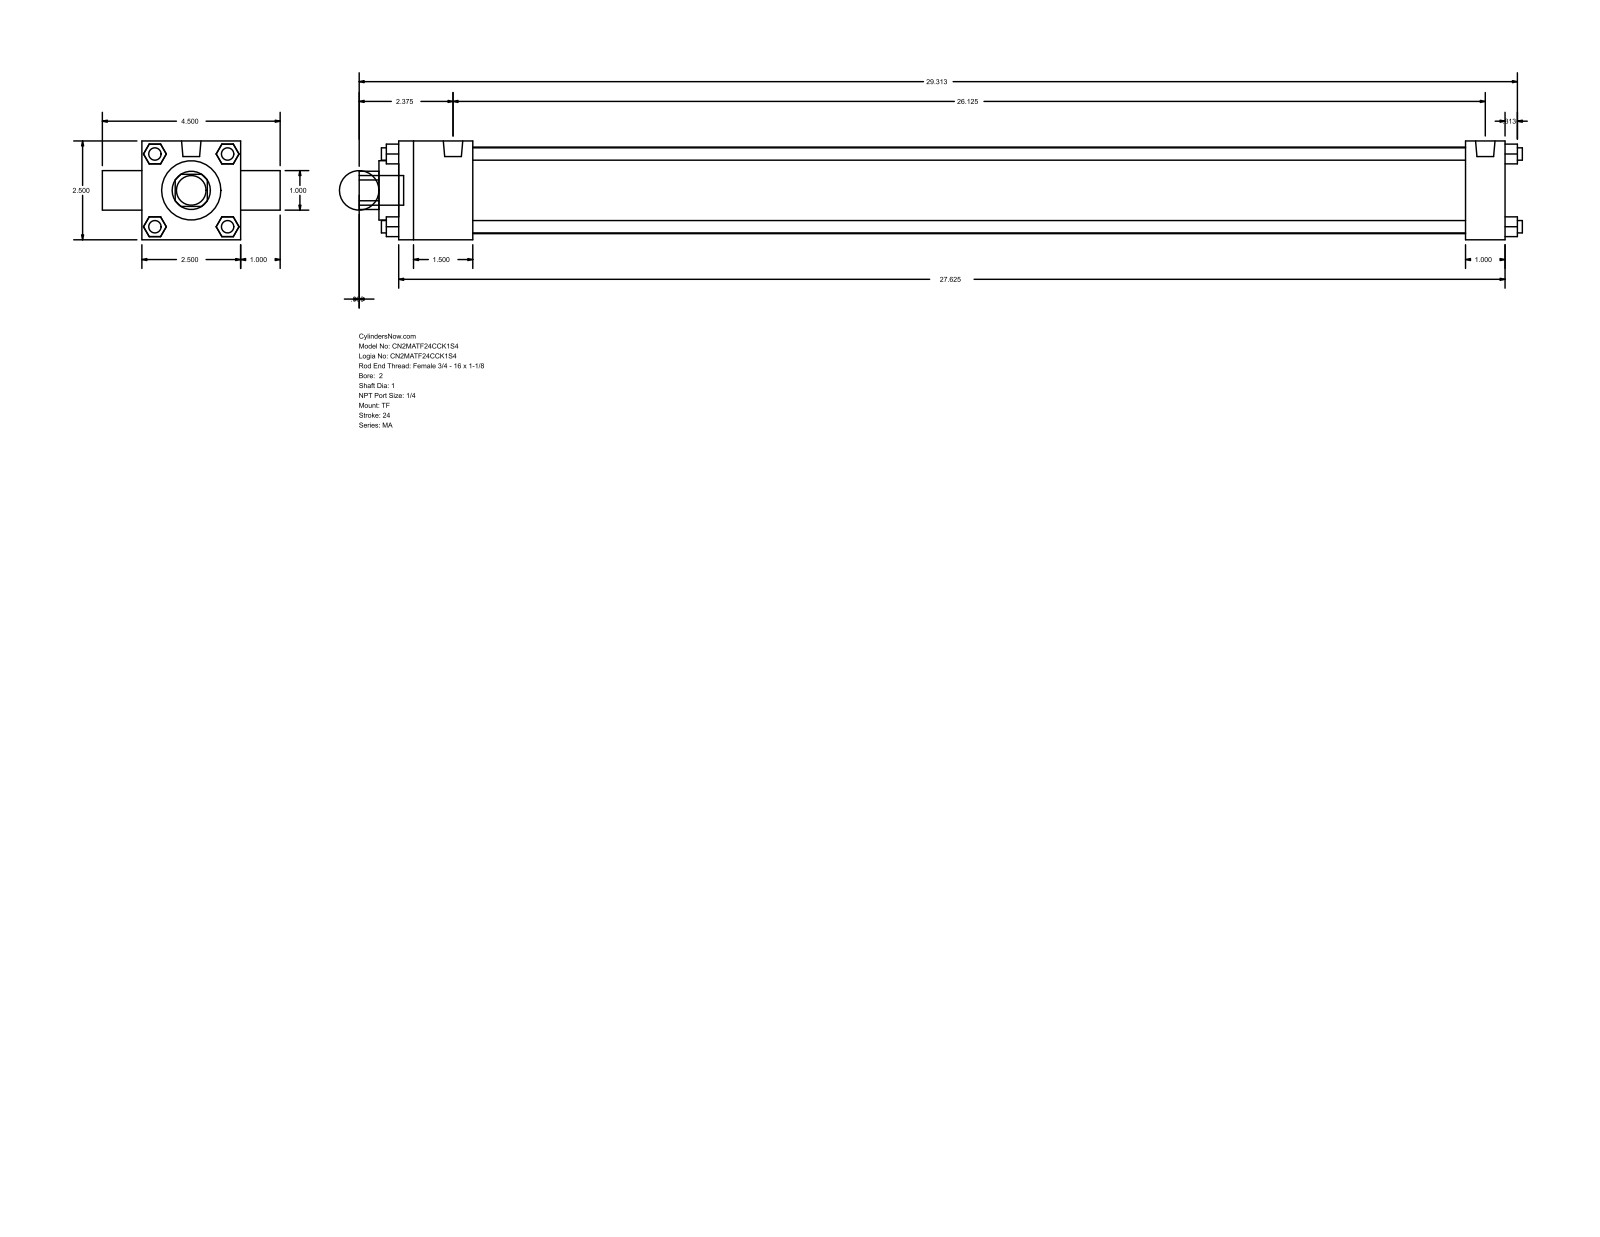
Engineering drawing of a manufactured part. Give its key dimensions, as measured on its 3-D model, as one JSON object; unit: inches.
{"part_name": "MA_TF__0200_1", "step_written_by": "GSSL Pune (CONFIG_CONTROL_DESIGN)", "units": "inches", "bodies": {"solids": 0, "faces": 120, "planar": 92, "cylindrical": 28, "other": 0}, "overall_size": [29.437, 4.5, 2.5], "round_holes": [[1, 2], [1.5, 1], [2.19, 1]], "round_bosses_or_shafts": [[0.313, 7], [0.492, 2], [0.75, 1]], "partial_cylinders_radius": [[0.484, 1]], "face_to_face_distances": [2.5, 1, 28, 0.5, 1.875, 27, 25.125, 26.125, 3.5, 1.593]}
